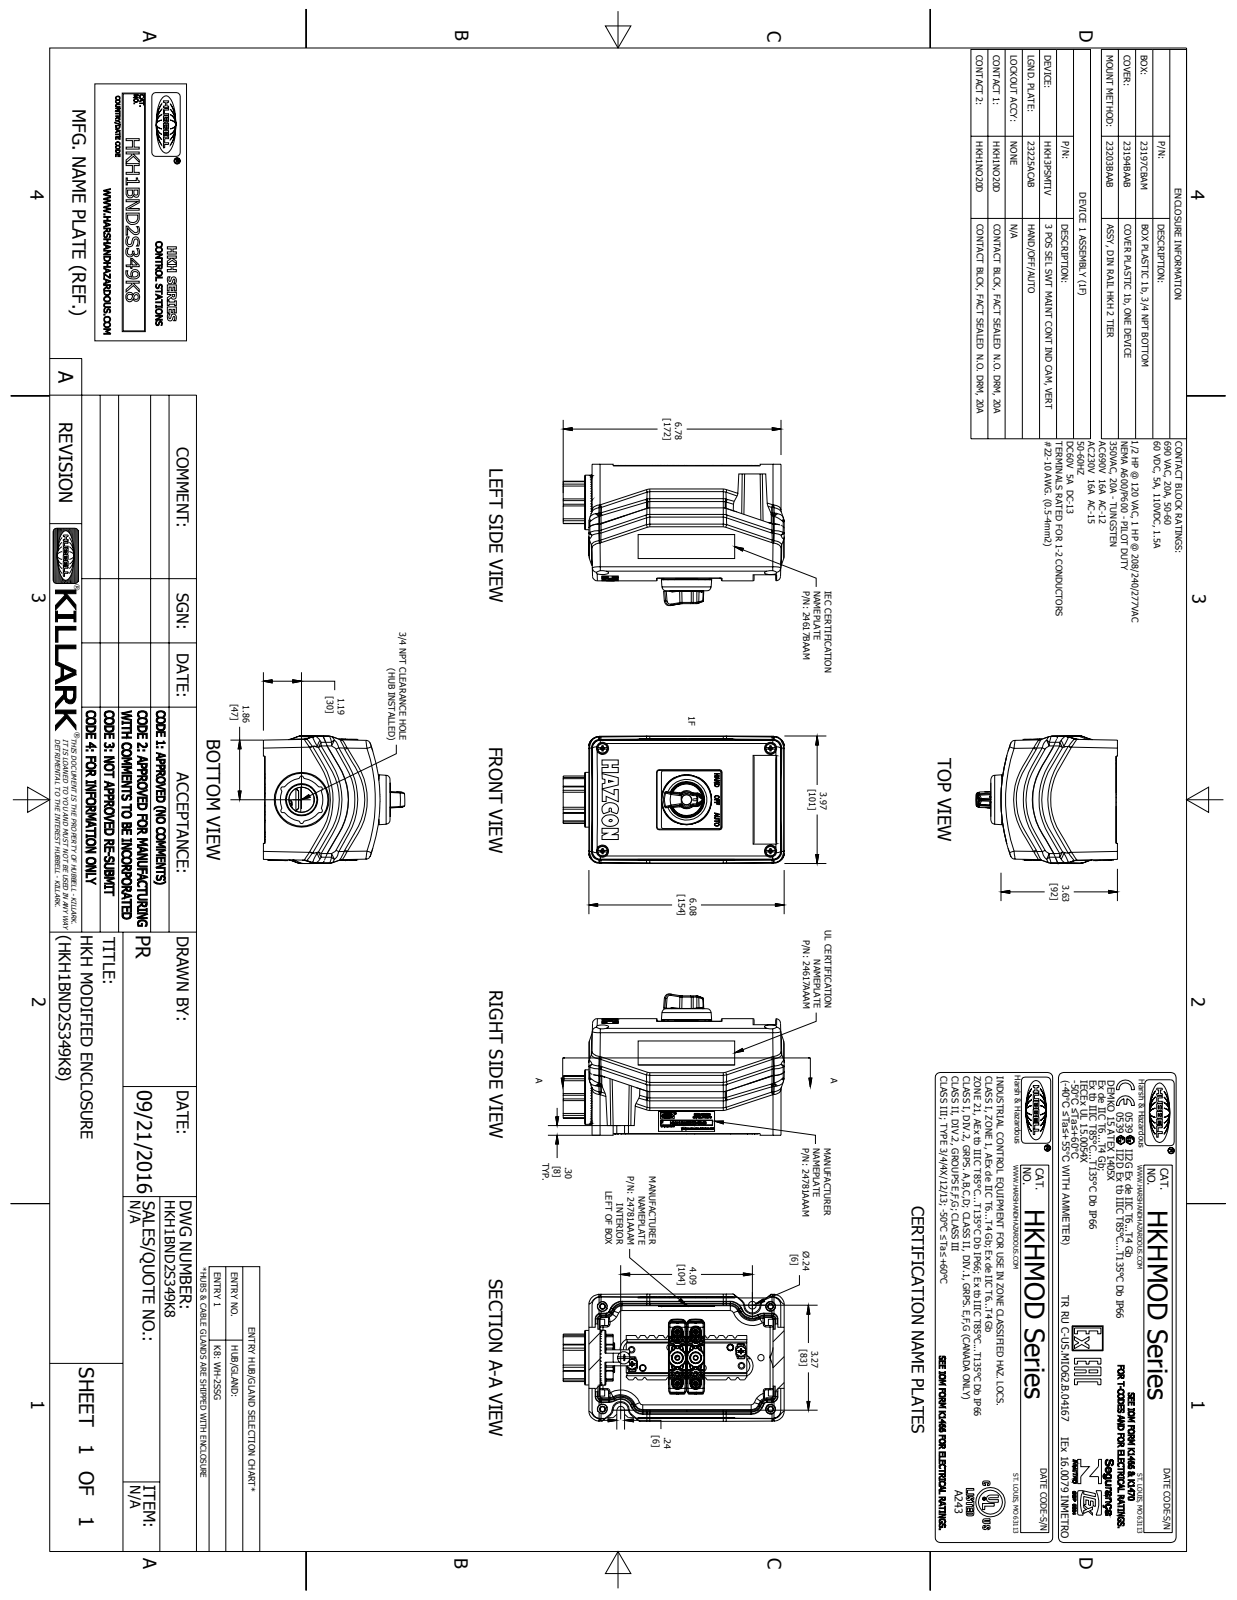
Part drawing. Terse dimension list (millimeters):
name: 23194BAAB.; 23197CBAM.; 24617AAAM; 24617BAAM (+8 more)
written by: Autodesk Inventor 2016 (AUTOMOTIVE_DESIGN)
unit: mm
bodies: 95 solids, 28715 faces (13891 planar, 4494 cylindrical, 10330 other)
size: 174.68 × 111.78 × 100.74
volume: 552 822 mm³; area: 266 346 mm²
holes: 16× ⌀4.7, 12× ⌀2.67, 8× ⌀1.5, 8× ⌀2.13, 8× ⌀3.05, 8× ⌀3.17, 8× ⌀5.33, 6× ⌀3.78, 6× ⌀5.46, 4× ⌀1, 4× ⌀2.03, 4× ⌀2.29
bosses: 13× ⌀4.57, 12× ⌀2.54, 8× ⌀1.47, 6× ⌀2.95, 4× ⌀8, 4× ⌀7.24, 4× ⌀7.11, 4× ⌀5.98
rounds: 647× R0.38, 607× R0.25, 475× R0.13, 237× R0.51, 114× R0.76, 90× R0.1, 52× R1.02, 42× R6.35
face distances: 6.35, 81.92, 7.49, 143.01, 95.61, 88.12, 75.57, 89.26, 81.77, 14.48
hole spacings: 4.83, 5.48, 6.61, 7.3, 11.44, 14.48, 15.26, 22.34
